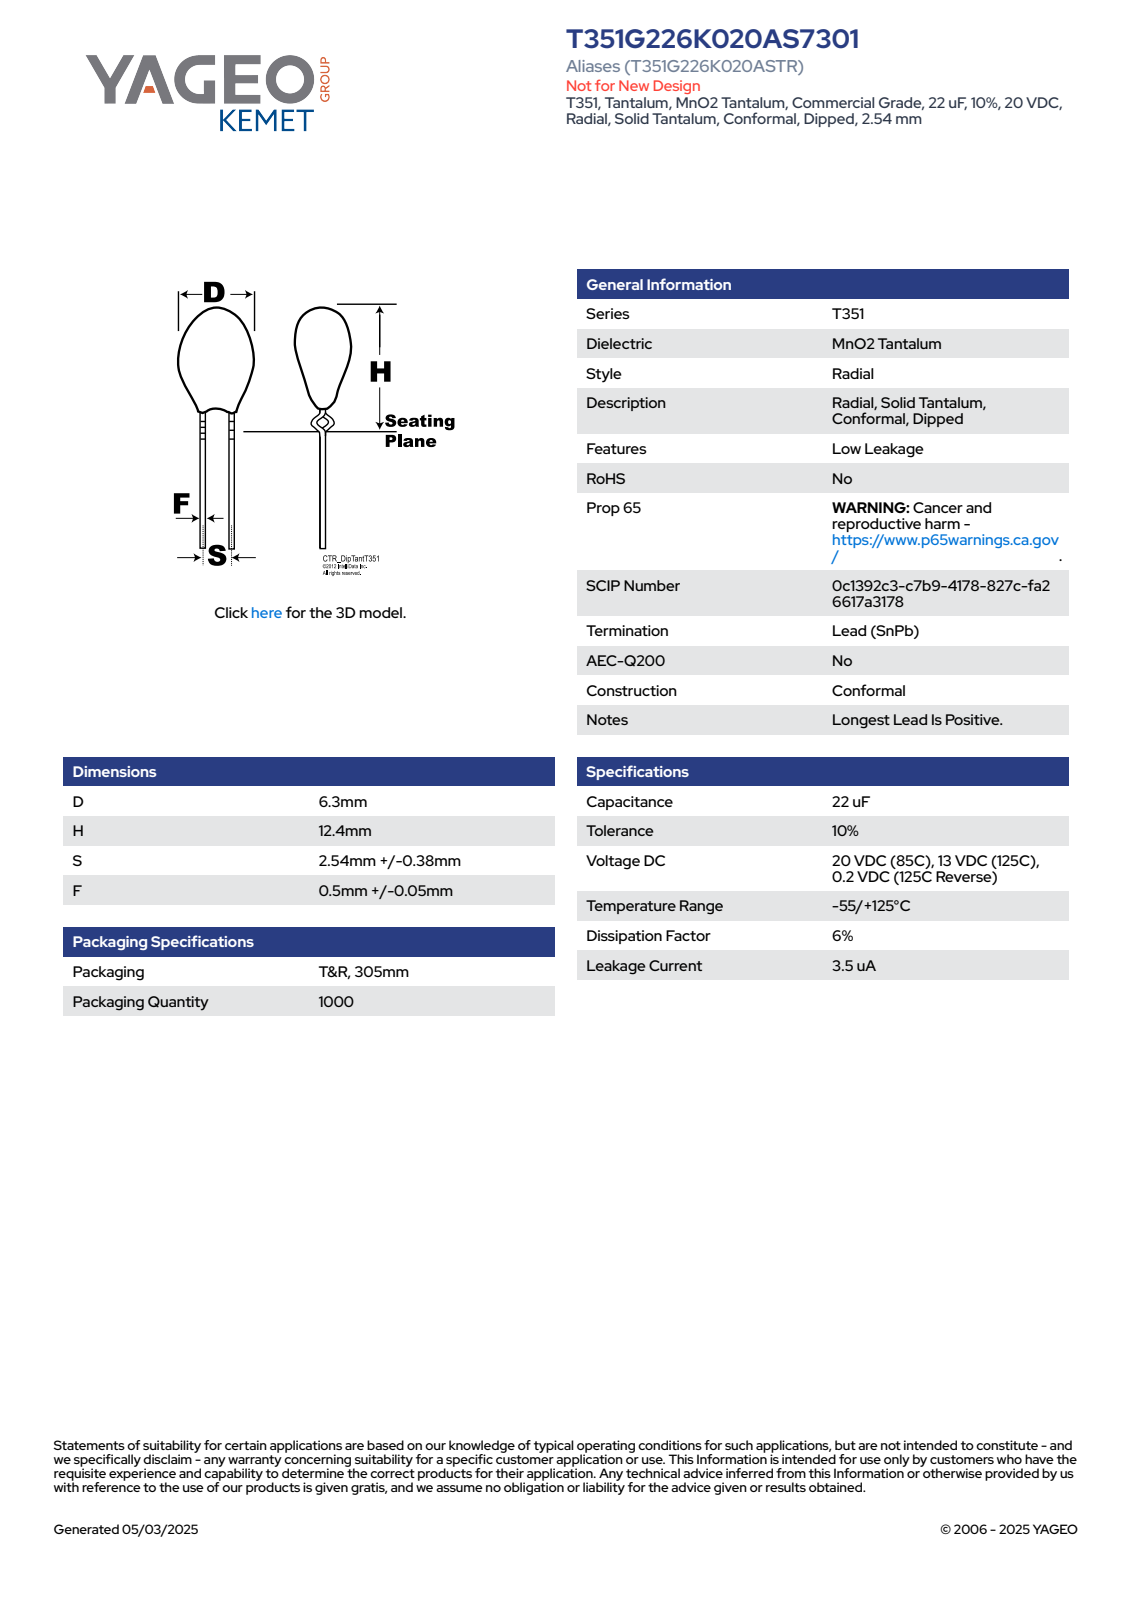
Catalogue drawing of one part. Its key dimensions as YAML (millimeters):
part_name: "CTR_T351_D6.3H12.4S2.54LL5.56F0.55"
step_written_by: "SolidWorks 2014 (AUTOMOTIVE_DESIGN)"
units: millimeters
bodies: {solids: 1, faces: 88, planar: 27, cylindrical: 10, other: 51}
overall_size: [17.96, 6.3, 6.3]
volume: 220
surface_area: 215
round_bosses_or_shafts:
  - {diameter: 0.55, count: 2}
  - {diameter: 6.3, count: 1}
partial_cylinders:
  - {radius: 3.14, count: 1}
face_to_face_distances: [8.92, 13.91, 4.99, 12.9, 3.98, 1.01, 0.44, 0.82, 0.63, 0.38]
